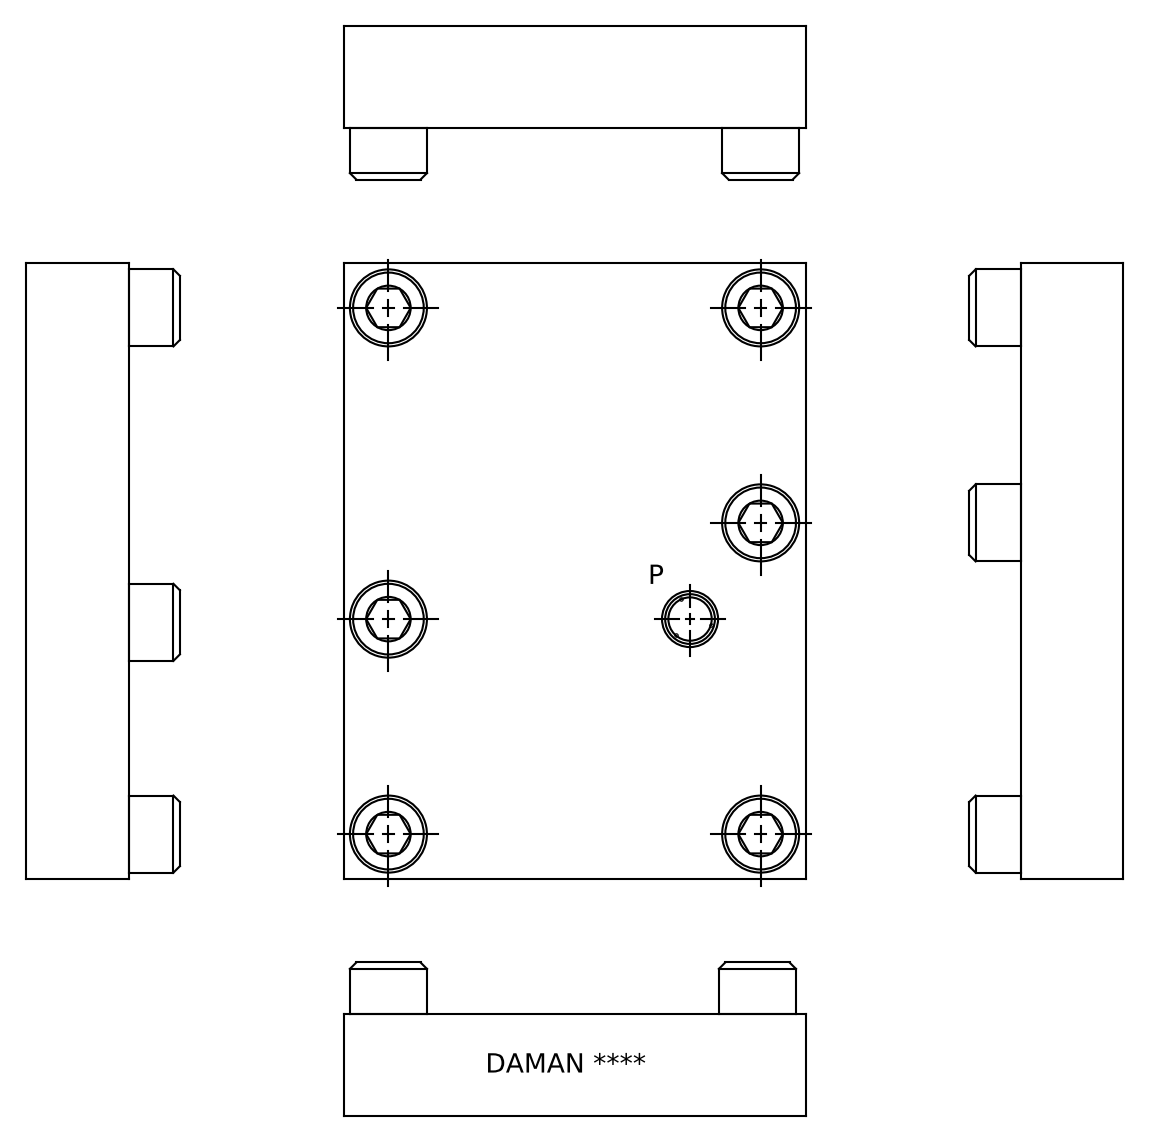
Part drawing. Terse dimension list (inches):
name: D08CPPG
written by: Autodesk Inventor 2020 (AUTOMOTIVE_DESIGN)
unit: in
bodies: 1 solid, 344 faces (225 planar, 16 cylindrical, 103 other)
size: 6 × 4.5 × 1
volume: 24.7 in³; area: 86.6 in²
holes: 6× ⌀0.531, 4× ⌀1.313, 2× ⌀0.25, 2× ⌀1, 1× ⌀0.422, 1× ⌀0.546
face distances: 1, 0.11, 0.89, 4.5, 6, 5.99, 0.551, 0.441, 0.449, 0.99
hole spacings: 1.162, 1.163, 1.345, 1.407, 1.875, 2.438, 3.157, 3.2
